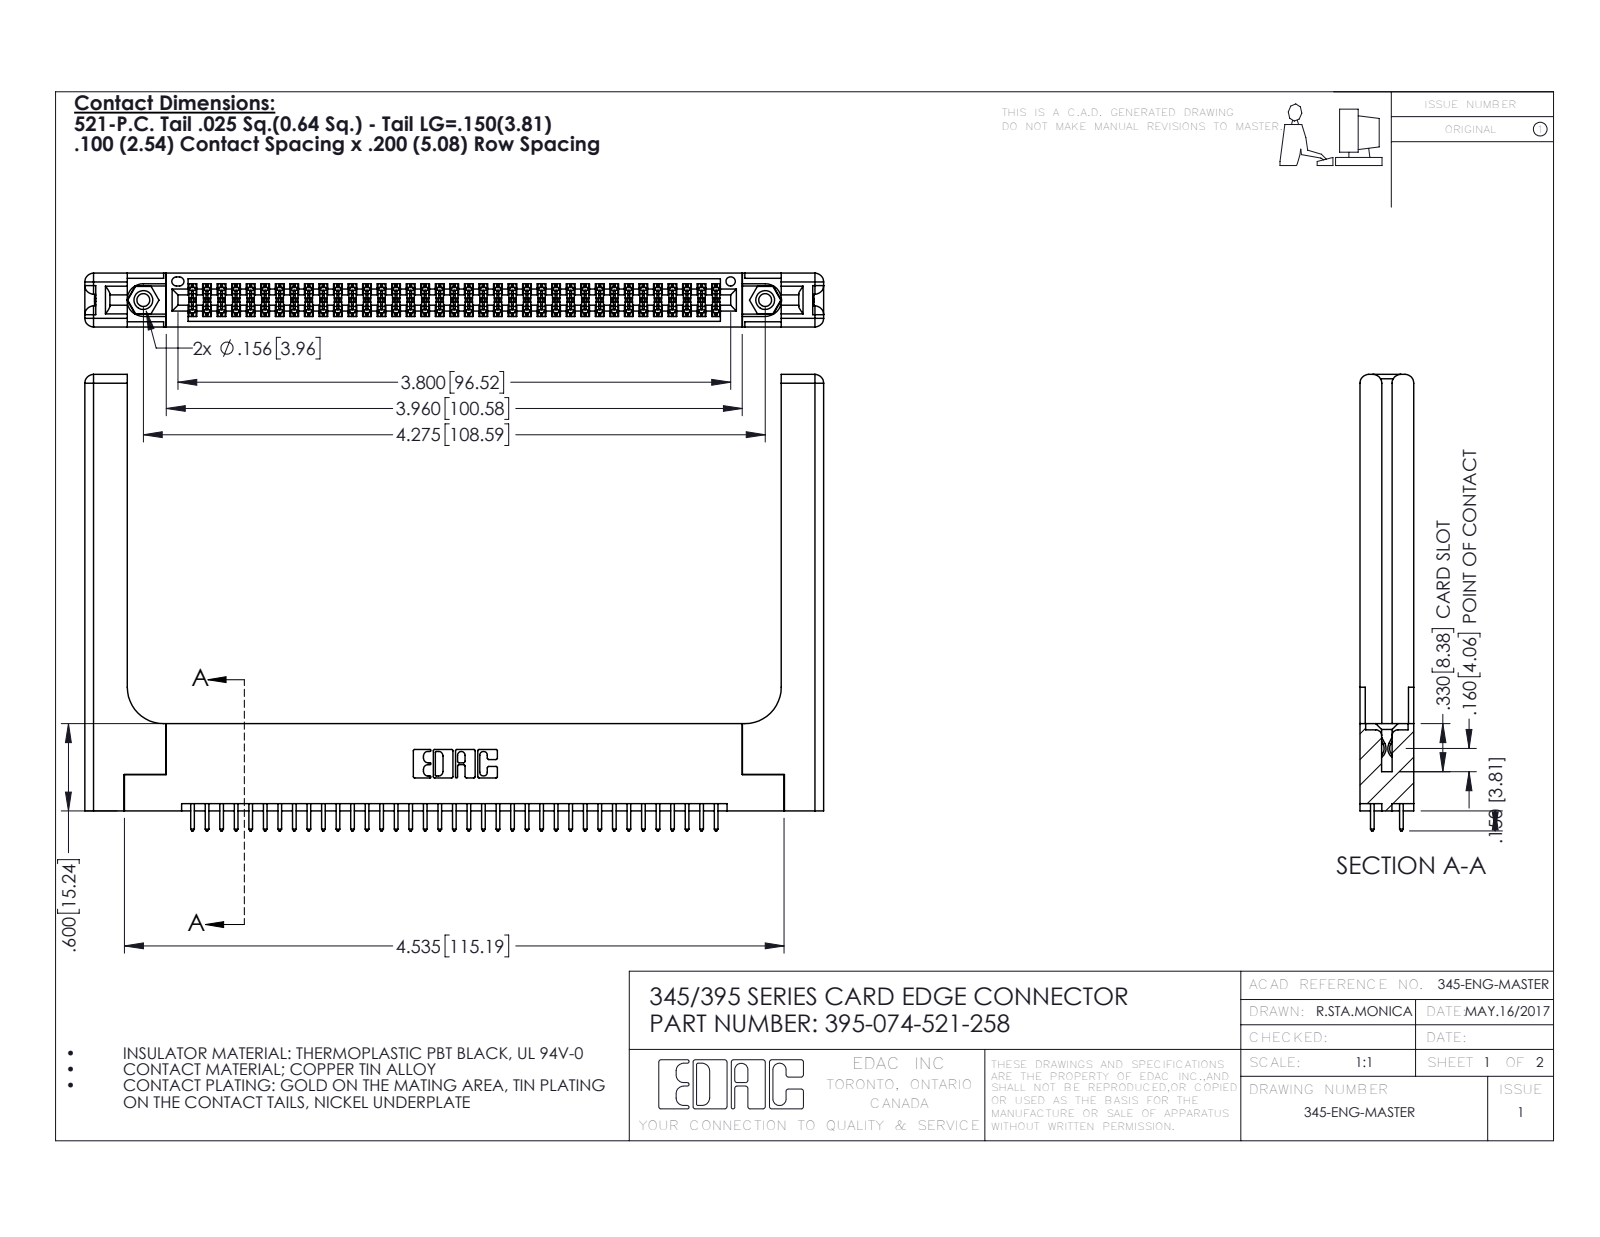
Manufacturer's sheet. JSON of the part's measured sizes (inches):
{"part_name": "345-292-001_345-293-121; 345 Part_Flush Mounting Lugs - 0.156 Dia-TH; 345-220-058_345-220-058; 345-250-001_345-250-001-102 (+1 more)", "step_written_by": "SolidWorks 2016 (CONFIG_CONTROL_DESIGN)", "units": "inches", "bodies": {"solids": 79, "faces": 4082, "planar": 2670, "cylindrical": 1352, "other": 60}, "overall_size": [5.079, 3.137, 0.37], "volume_in3": 1.277, "surface_area_in2": 35.92, "round_holes": [[0.089, 2], [0.125, 2], [0.156, 2], [0.064, 1]], "round_bosses_or_shafts": [[0.155, 2]], "partial_cylinders_radius": [[0.006, 111], [0.01, 74], [0.01, 22], [0.06, 16], [0.007, 6], [0.031, 6], [0.026, 3], [0.014, 2]], "face_to_face_distances": [0.072, 0.37, 0.298, 0.2, 0.098, 0.272, 0.025, 0.225, 0.148, 0.15], "hole_center_spacings": [0.27, 4.039, 4.275]}
